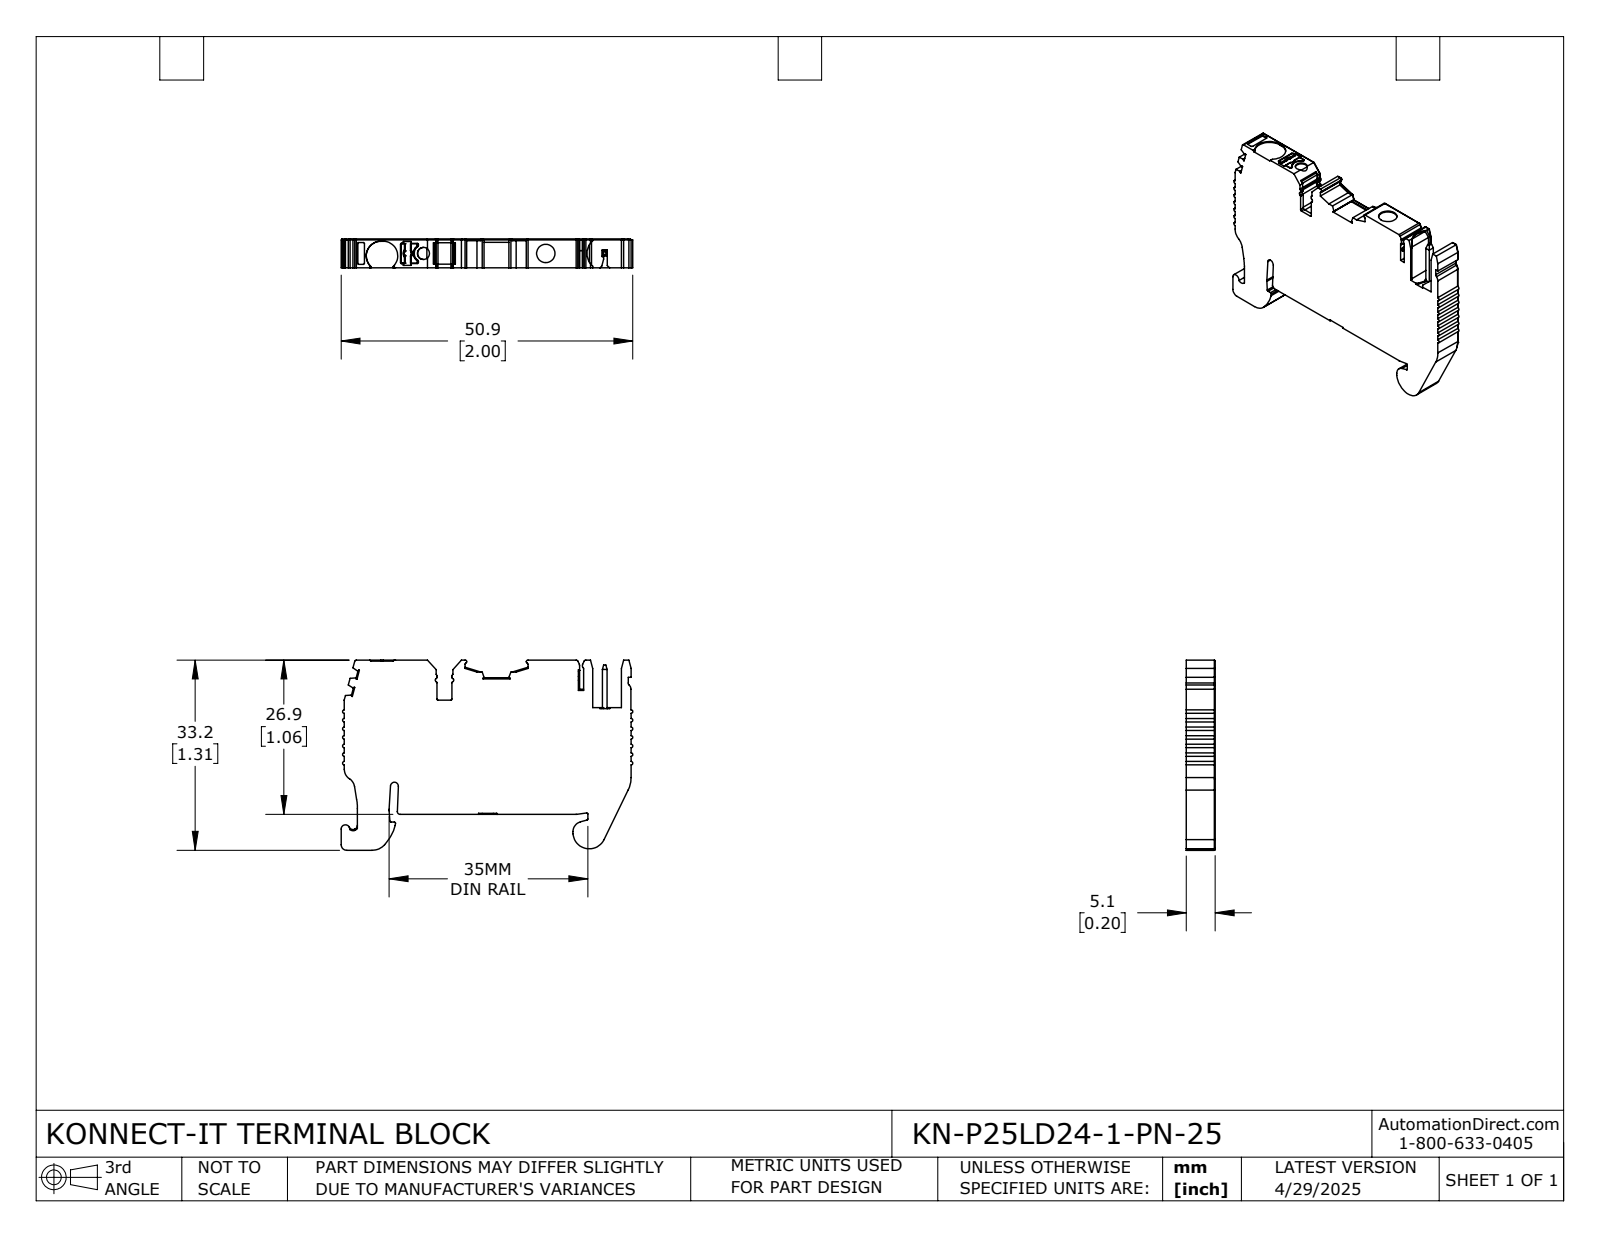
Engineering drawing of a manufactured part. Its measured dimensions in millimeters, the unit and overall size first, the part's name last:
Units: millimetres
Overall size (bounding box): 50.92 × 33.21 × 5.05
Round holes (diameter × count): ⌀2.1 ×1, ⌀3.2 ×1
Partial cylindrical surfaces — rounded edges, fillets, slot ends (radius × count): R0.3 ×35, R0.2 ×34, R0.5 ×13, R0.1 ×9, R0.4 ×8, R0.15 ×4, R0.6 ×3, R0.9 ×3
Main face-to-face distances: 5.05, 26.95, 26.75, 50.07, 48.38, 1.69, 24.91, 5.2, 43.18, 6.89
Hole centre spacings: 21.35
Volume: 6 509 mm³ · Surface area: 3 879 mm²
Bodies: 1 solid, 461 faces (263 planar, 179 cylindrical, 19 other)
Part name (STEP PRODUCT): KN-P25LD24-1-PN-25
STEP written by: SolidWorks 2024 (CONFIG_CONTROL_DESIGN)
